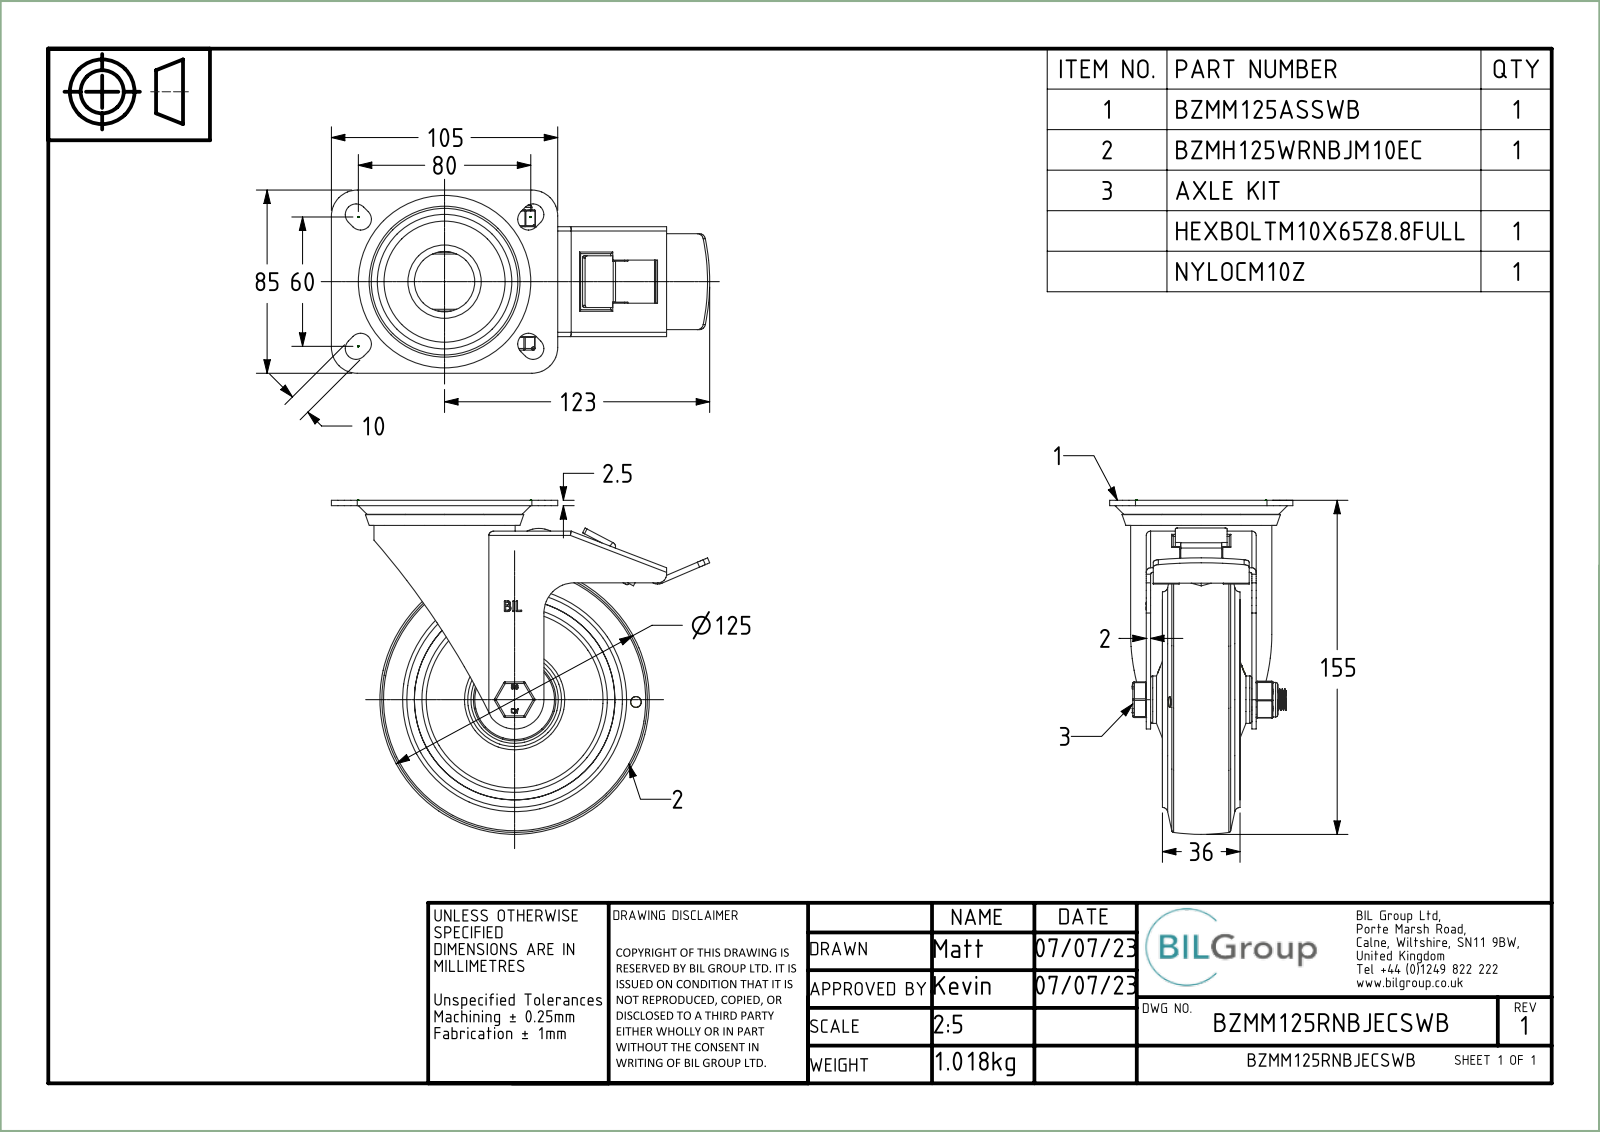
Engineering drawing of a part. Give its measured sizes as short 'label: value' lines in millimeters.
name: BZMM125ASSWB - 47; ZINC PLATED, PRESSED STEEL TOP PLATE; ZINC PLATED, PRESSED STEEL FORKS; BEARING SEAL (+8 more)
written by: Spatial InterOp 3D (CONFIG_CONTROL_DESIGN)
unit: mm
bodies: 31 solids, 1347 faces (475 planar, 503 cylindrical, 369 other)
size: 175.5 × 155 × 85
volume: 345 376 mm³; area: 175 715 mm²
holes: 2× ⌀4, 2× ⌀6, 1× ⌀5, 1× ⌀10, 1× ⌀10.2, 1× ⌀12, 1× ⌀15, 1× ⌀20, 1× ⌀22.5, 1× ⌀25.5, 1× ⌀28, 1× ⌀30
bosses: 1× ⌀65.5, 1× ⌀43.5, 1× ⌀38.25, 1× ⌀34.5, 1× ⌀34, 1× ⌀30.5, 1× ⌀28, 1× ⌀23
rounds: 18× R0.5, 16× R0.75, 12× R1.5, 9× R5, 8× R1, 6× R2, 5× R12, 4× R3
face distances: 2, 7.5, 4, 23.5, 21.5, 25.5, 49, 27.5, 5, 16
hole spacings: 43.75
